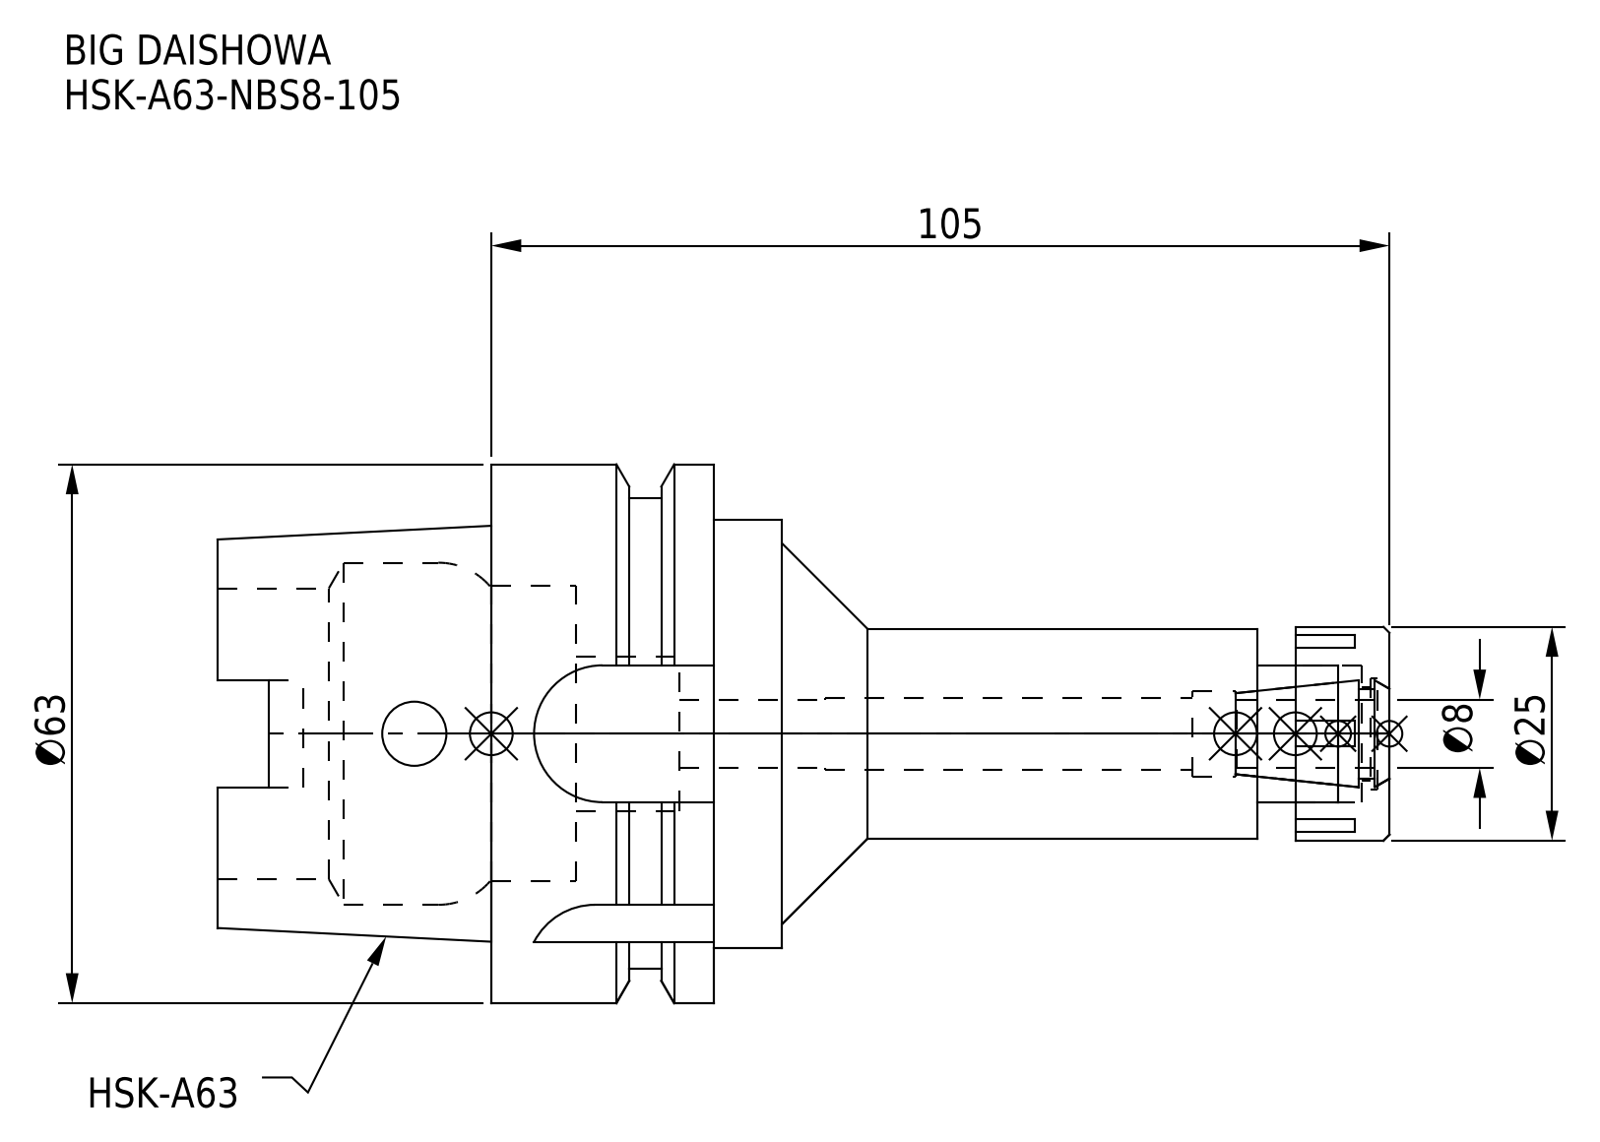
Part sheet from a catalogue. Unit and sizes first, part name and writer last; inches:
Units: inches
Overall size (bounding box): 5.394 × 2.48 × 2.48
Round holes (diameter × count): ⌀0.295 ×1, ⌀0.315 ×1, ⌀0.331 ×1, ⌀0.394 ×1, ⌀0.433 ×1, ⌀0.512 ×1, ⌀0.63 ×1, ⌀0.709 ×1, ⌀1.339 ×1, ⌀1.358 ×1, ⌀1.575 ×1
Round bosses / shafts (diameter × count): ⌀2.48 ×1, ⌀2.165 ×1, ⌀1.969 ×1, ⌀0.984 ×1, ⌀0.965 ×1
Partial cylindrical surfaces — rounded edges, fillets, slot ends (radius × count): R0.113 ×4, R0.315 ×4
Main face-to-face distances: 1.024, 0.632, 0.392, 2.283, 1.652, 1.26, 0.315, 0.947, 1.339, 2.598
Volume: 7.877 in³ · Surface area: 50.11 in²
Bodies: 2 solids, 141 faces (70 planar, 49 cylindrical, 22 other)
Part name (STEP PRODUCT): DXF_TEMP_ASSY_ASM_4_ASM.stp; HSK-A63-NBS8-105; HSK-A63-NBS8-105.stp; HA63NB08105-080_ASM.stp (+3 more)
STEP written by: SolidWorks 2019 (CONFIG_CONTROL_DESIGN)
